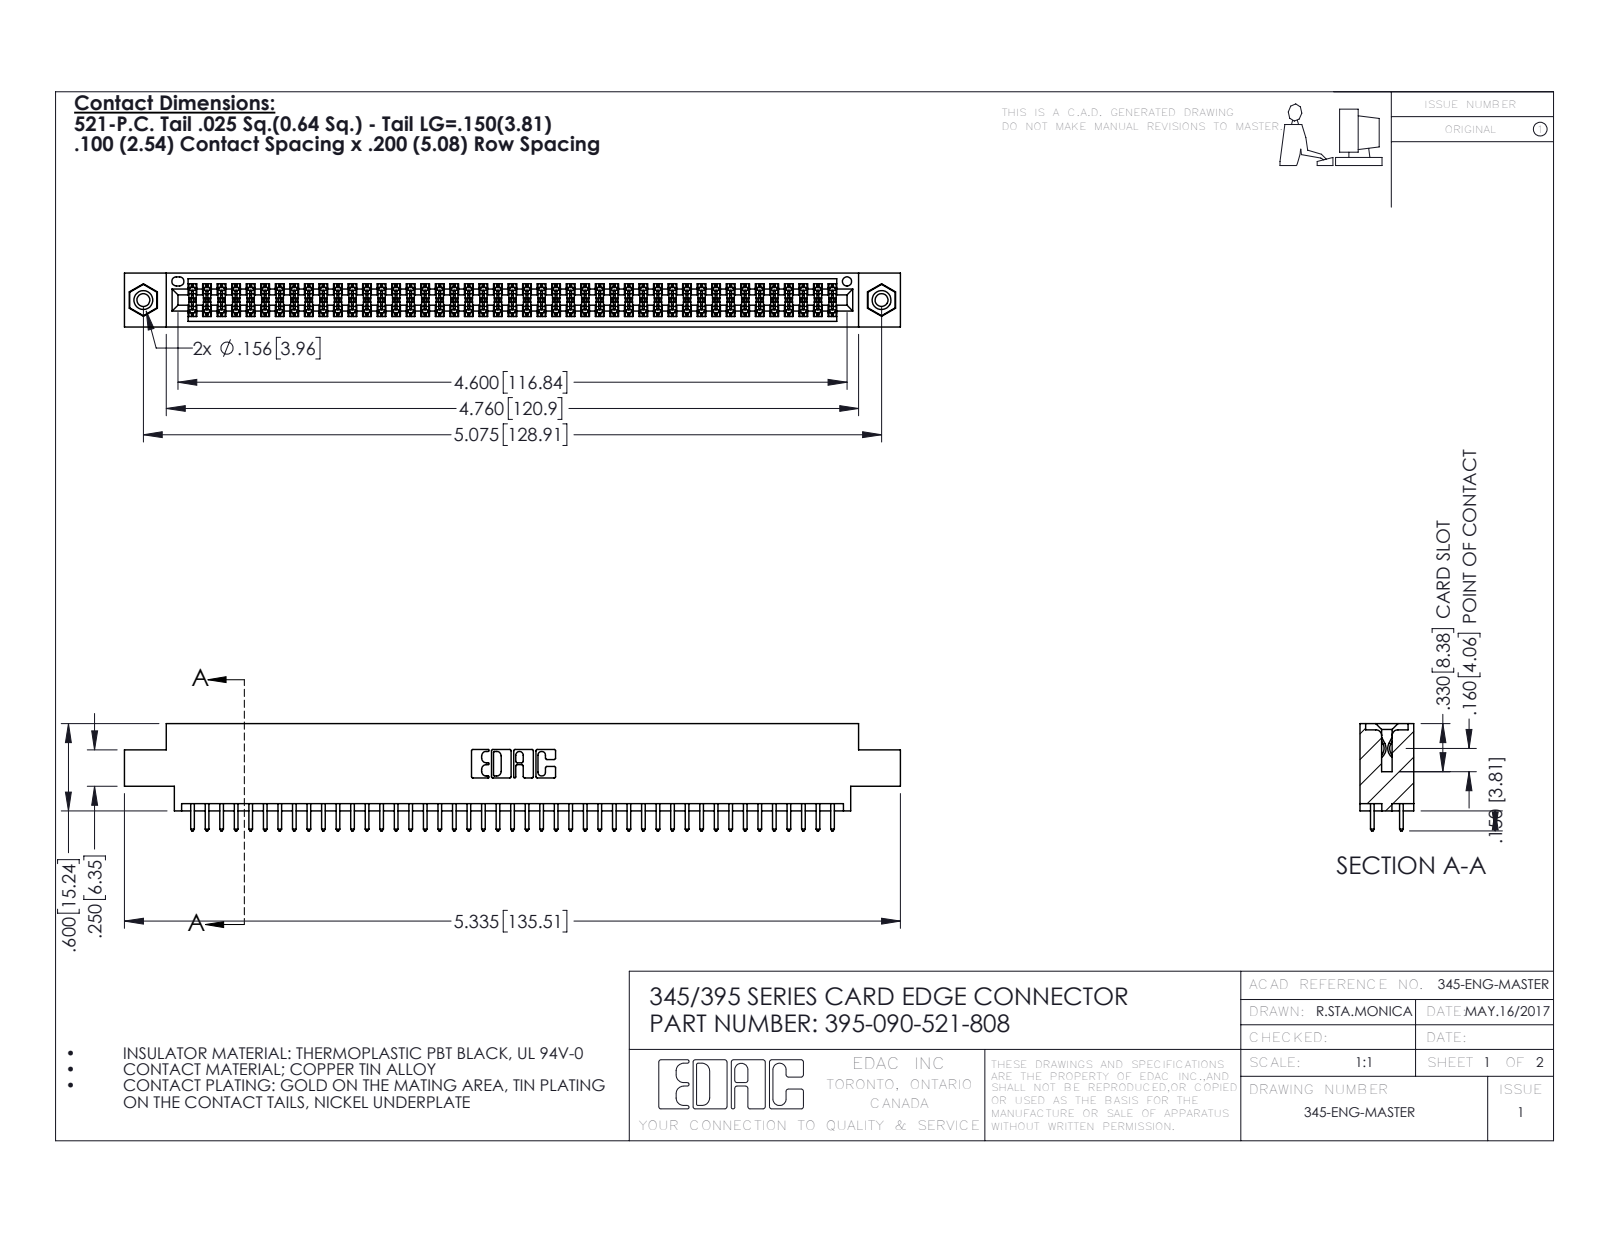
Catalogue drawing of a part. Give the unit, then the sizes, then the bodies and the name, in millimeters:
Units: millimetres
Overall size (bounding box): 135.5 × 18.7 × 9.4
Round holes (diameter × count): ⌀2.3 ×2, ⌀3.2 ×2, ⌀4 ×2, ⌀1.6 ×1
Round bosses / shafts (diameter × count): ⌀3.9 ×2
Partial cylindrical surfaces — rounded edges, fillets, slot ends (radius × count): R0.2 ×135, R0.3 ×90, R0.3 ×22, R0.2 ×6, R0.8 ×6, R0.7 ×3, R0.4 ×2, R0.5 ×2
Main face-to-face distances: 1.8, 7.6, 5.1, 9.4, 2.5, 6.9, 0.6, 5.7, 4.4, 3.8
Hole centre spacings: 6.9, 122.9, 128.9
Volume: 13 000 mm³ · Surface area: 19 250 mm²
Bodies: 93 solids, 4690 faces (3086 planar, 1588 cylindrical, 16 other)
Part name (STEP PRODUCT): 345-292-001_345-293-121; 345-250-001_345-250-003-102; 345 Part_0.170 Offset - 0.156 Dia-TI; 395-090-521-808
STEP written by: SolidWorks 2016 (CONFIG_CONTROL_DESIGN)
